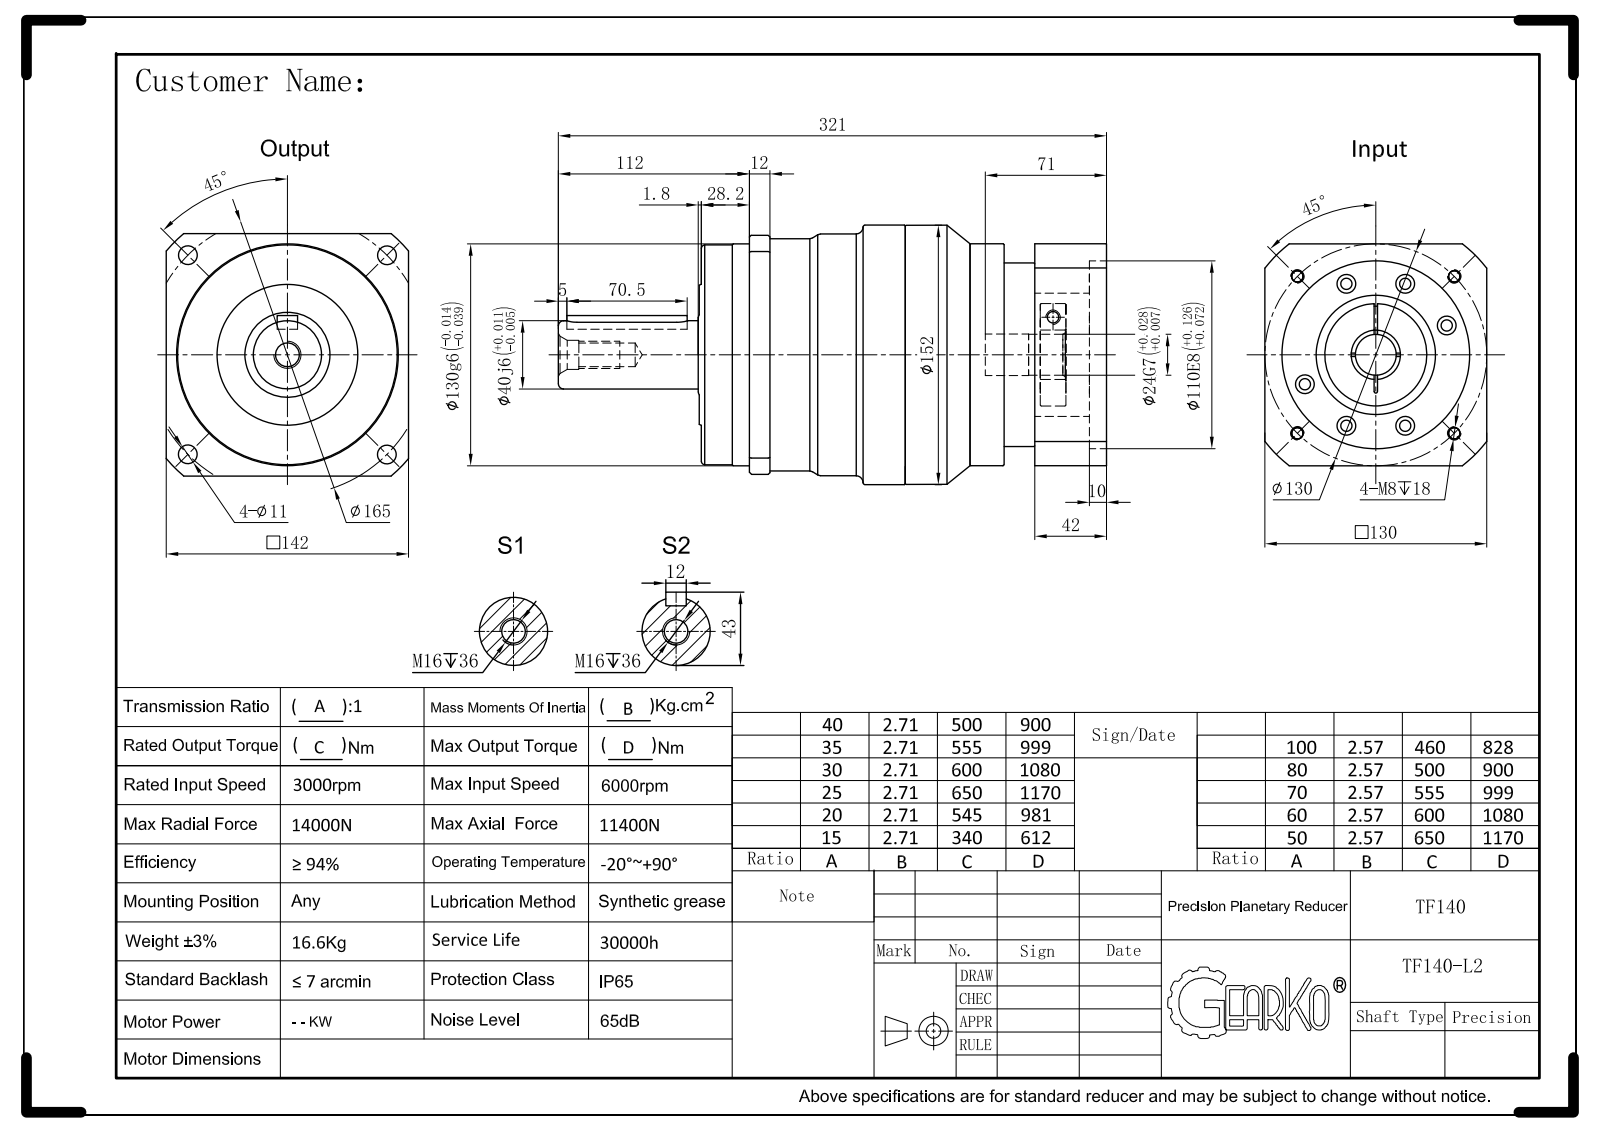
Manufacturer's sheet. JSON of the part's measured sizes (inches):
{"step_written_by": "SolidWorks 2017 (CONFIG_CONTROL_DESIGN)", "units": "inches", "bodies": {"solids": 4, "faces": 229, "planar": 58, "cylindrical": 81, "other": 90}, "overall_size": [12.65, 5.984, 5.984], "volume_in3": 217.2, "surface_area_in2": 337.8, "round_holes": [[0.268, 4], [0.433, 4], [0.524, 1], [0.551, 1], [0.63, 1], [0.669, 1], [0.945, 1], [1.142, 1], [1.583, 1], [1.969, 1], [2.756, 1], [3.937, 1]], "round_bosses_or_shafts": [[5.984, 1], [5.571, 1], [5.354, 1], [5.118, 1], [5.071, 1], [4.232, 1], [2.362, 1], [1.575, 1]], "partial_cylinders_radius": [[0.02, 4], [0.236, 3], [0.039, 1], [3.248, 1], [3.642, 1]], "face_to_face_distances": [7.815, 7.697, 0.118, 5.118, 1.654, 9.35, 1.535, 1.142, 1.26, 1.11], "hole_center_spacings": [4.135, 2.559, 3.619, 5.807, 0.689, 0.689, 3.248, 3.248]}
